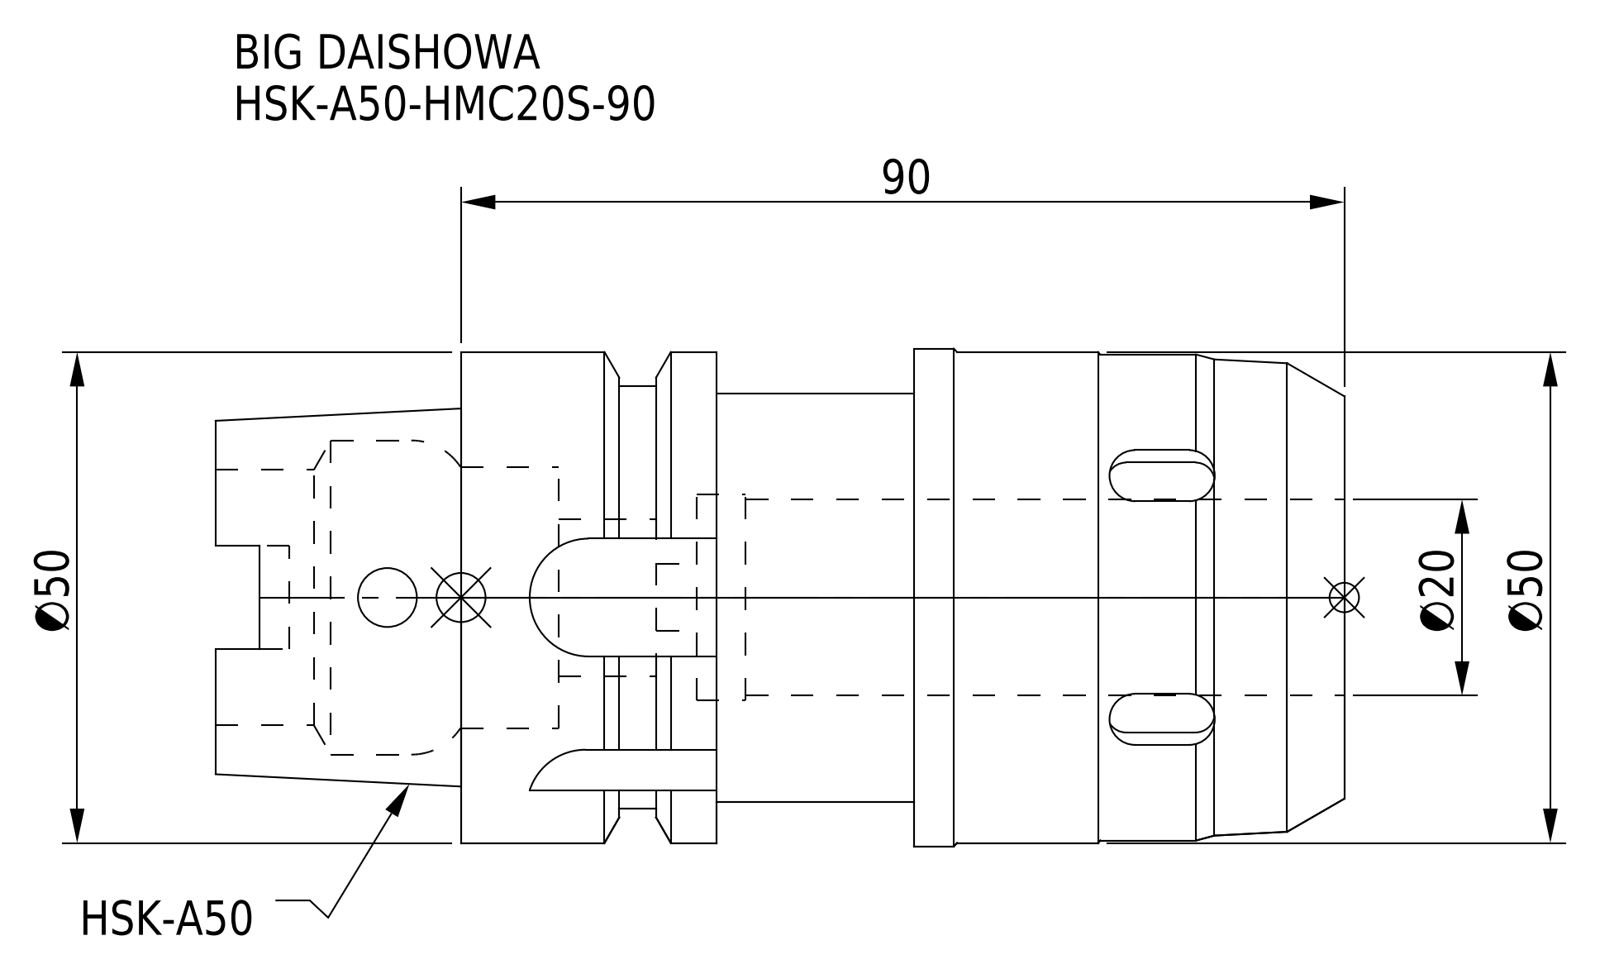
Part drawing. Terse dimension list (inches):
name: HSK-A50-HMC20S-90
written by: CREO PARAMETRIC BY PTC INC, 2016380 (AUTOMOTIVE_DESIGN)
unit: in
bodies: 1 solid, 138 faces (57 planar, 55 cylindrical, 26 other)
size: 4.528 × 1.996 × 1.996
volume: 8.366 in³; area: 46.29 in²
holes: 1× ⌀0.236, 1× ⌀0.268, 1× ⌀0.63, 1× ⌀0.787, 1× ⌀0.827, 1× ⌀1.024, 1× ⌀1.047, 1× ⌀1.26
bosses: 1× ⌀1.996, 1× ⌀1.969, 1× ⌀1.949, 1× ⌀1.693, 1× ⌀1.638
rounds: 6× R0.118, 4× R0.094, 4× R0.236
face distances: 3.543, 1.724, 1.819, 2.52, 0.795, 1.024, 4.528, 2.803, 2.008, 0.984
